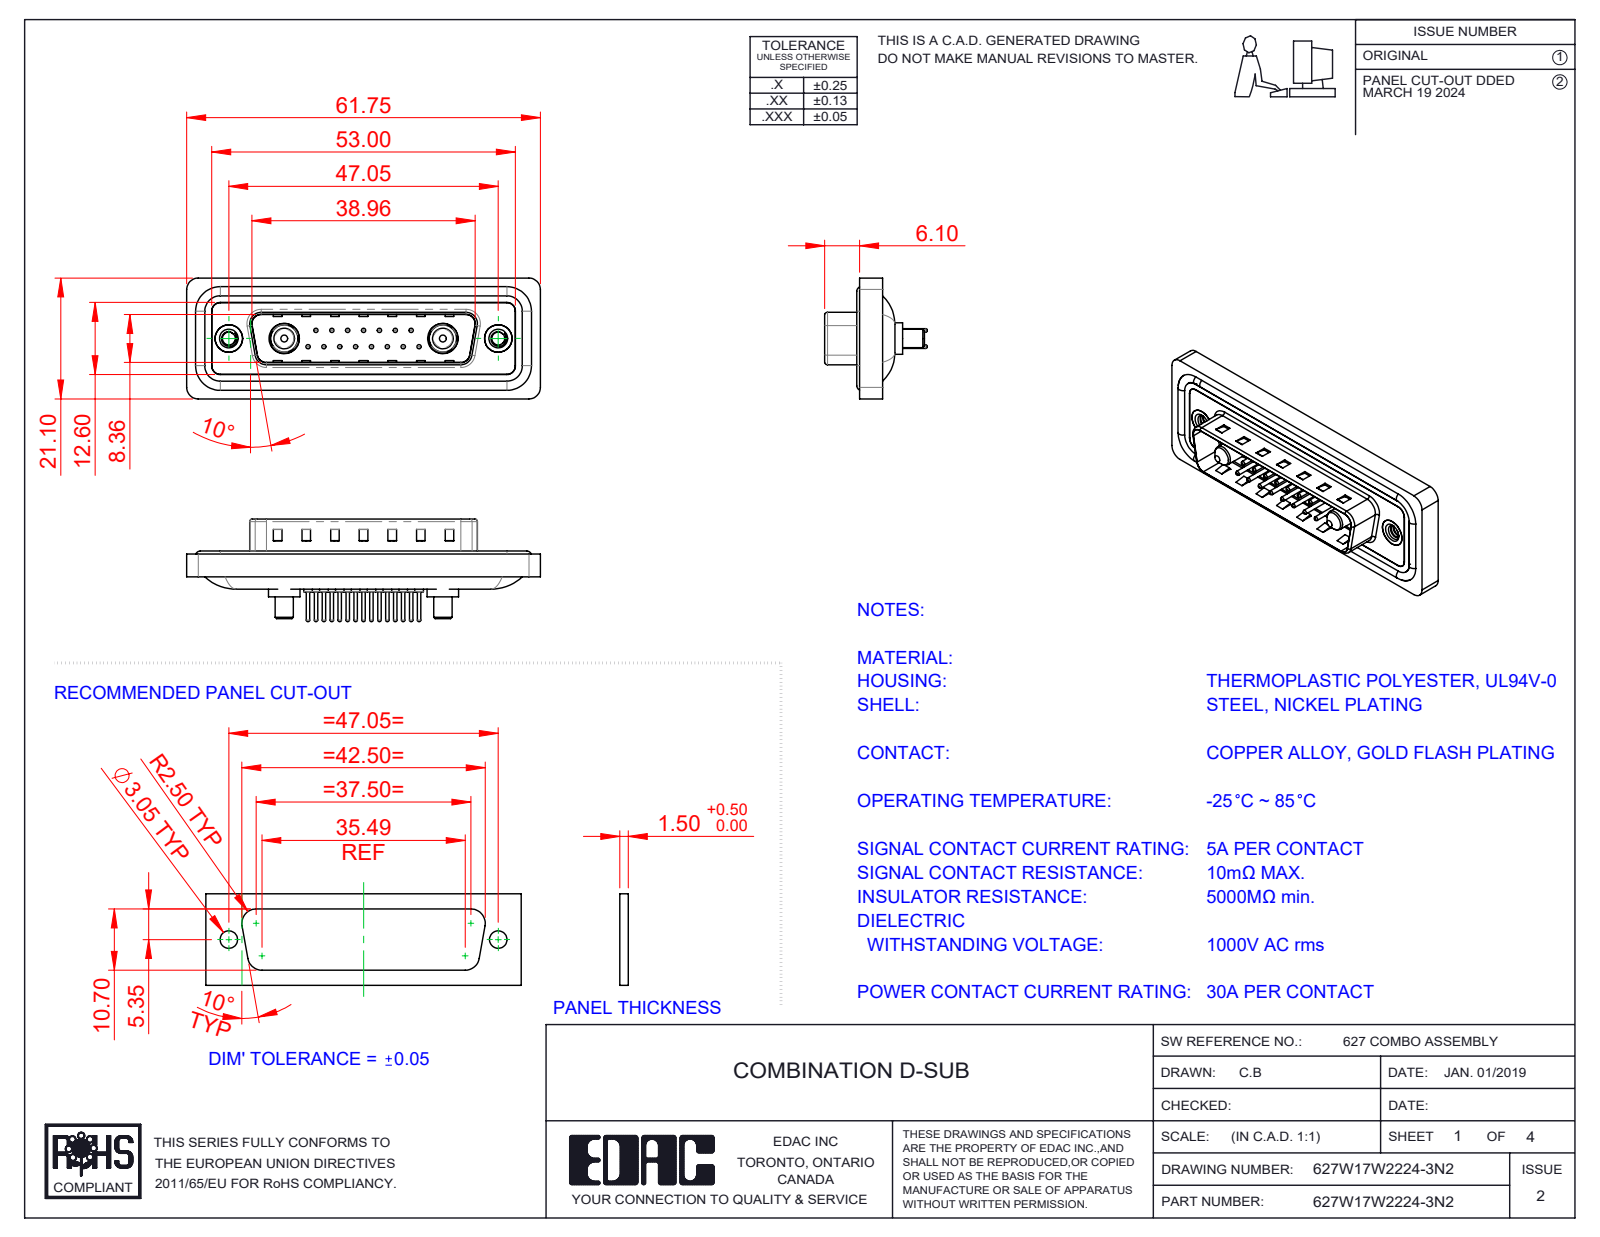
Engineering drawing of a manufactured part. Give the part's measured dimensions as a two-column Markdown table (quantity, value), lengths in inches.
| quantity | value |
| --- | --- |
| part name | 627W17W2224-3N2; 627Combo Shell Rear_25 Contacts; 627Combo Contact Row 1_24; Power Pin_30A S (+5 more) |
| STEP written by | SolidWorks 2023 (CONFIG_CONTROL_DESIGN) |
| units | inches |
| bodies | 26 solids, 1116 faces (334 planar, 436 cylindrical, 346 other) |
| overall size | 2.431 × 0.831 × 0.705 |
| volume | 0.444 in³ |
| surface area | 18.48 in² |
| round holes (diameter × count) | 0.03 × 15, 0.063 × 15, 0.079 × 15, 0.089 × 2, 0.157 × 2, 0.189 × 2, 0.191 × 2, 0.197 × 2, 0.209 × 2 |
| round bosses / shafts (diameter × count) | 0.059 × 15, 0.024 × 15, 0.063 × 4, 0.217 × 2, 0.205 × 2, 0.193 × 2, 0.187 × 2, 0.148 × 2 |
| partial cylindrical surfaces (radius × count) | 0.059 × 22, 0.079 × 18, 0.02 × 8, 0.063 × 8, 0.01 × 4, 0.024 × 4, 0.026 × 4, 0.035 × 4 |
| main face-to-face distances | 0.016, 0.059, 0.043, 0.063, 0.02, 0.122, 0.114, 0.032, 0.377, 0.161 |
| hole center spacings | 0.124, 0.109, 0.218, 0.327, 0.198, 0.295, 0.436, 0.198 |
